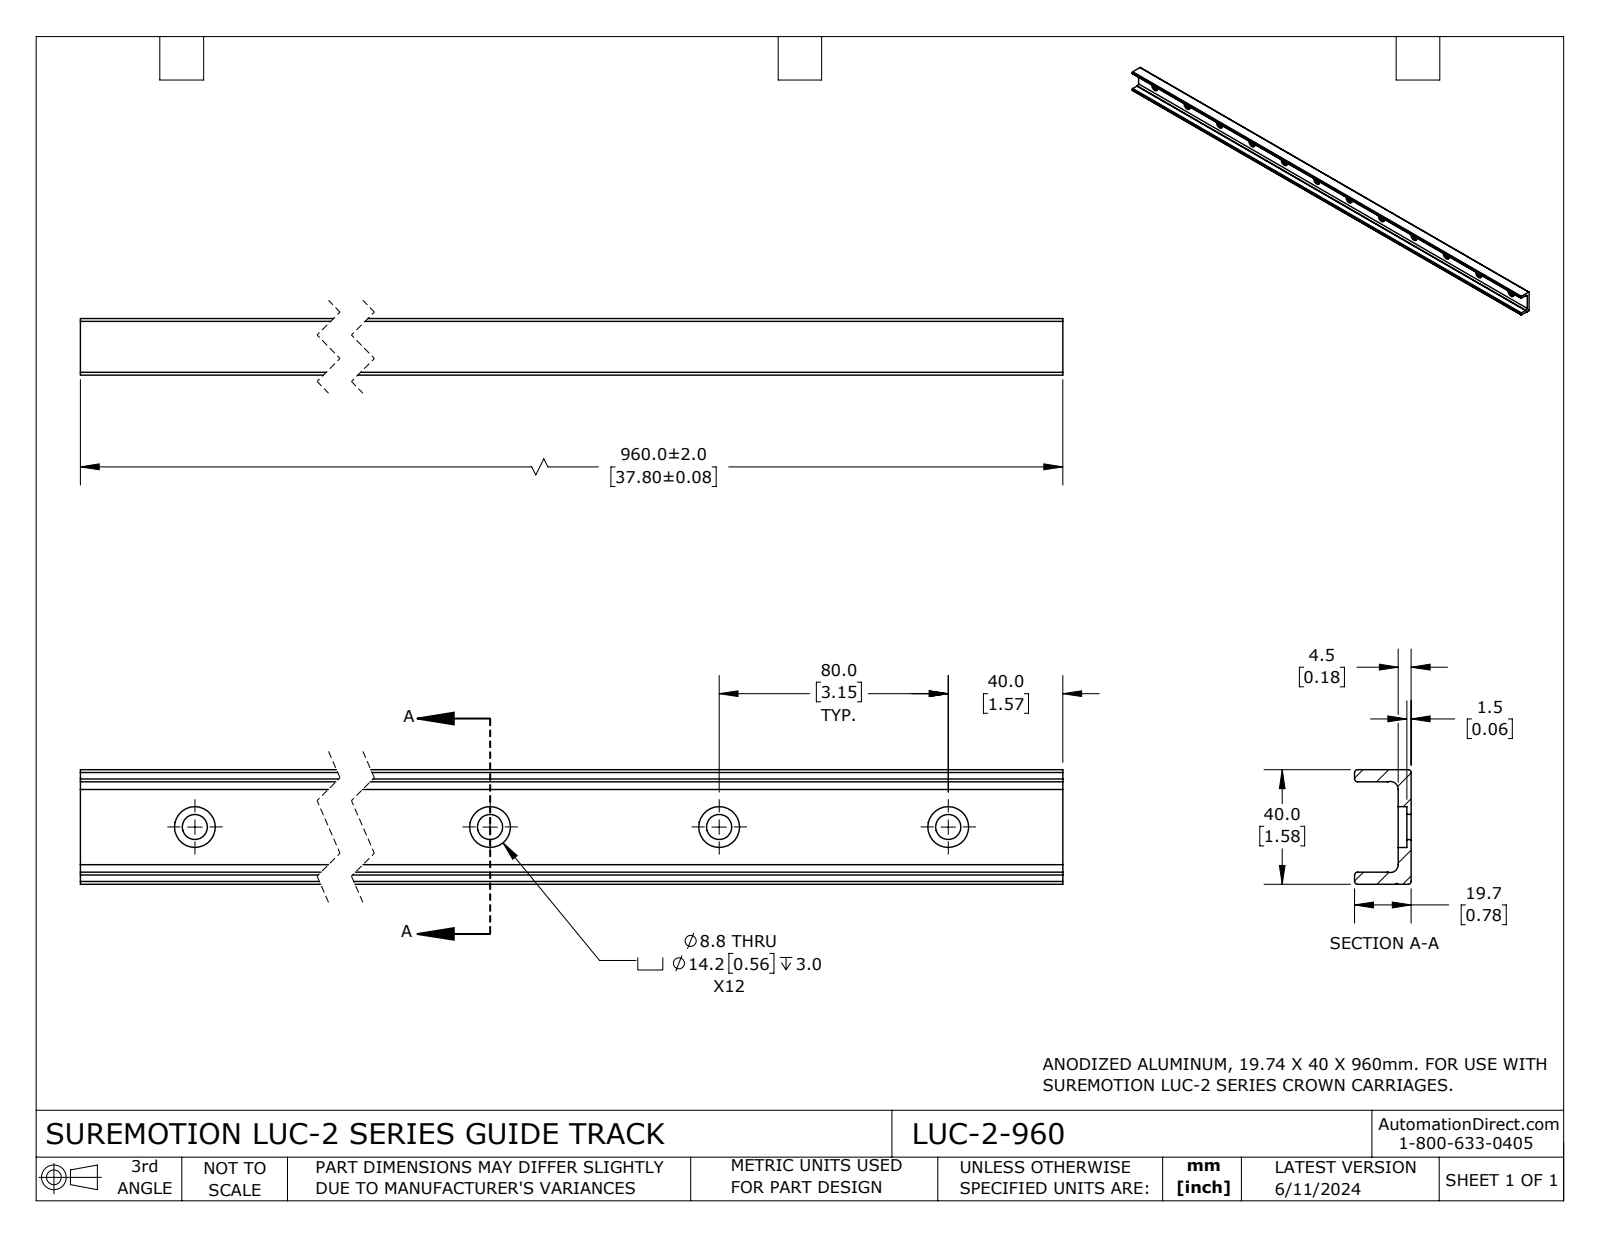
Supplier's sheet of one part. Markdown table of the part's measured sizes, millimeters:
| quantity | value |
| --- | --- |
| part name | LUC-2-960 |
| STEP written by | SolidWorks 2023 (CONFIG_CONTROL_DESIGN) |
| units | millimeters |
| bodies | 1 solid, 82 faces (23 planar, 59 cylindrical, 0 other) |
| overall size | 960 × 40.01 × 19.74 |
| volume | 291 320 mm³ |
| surface area | 141 193 mm² |
| round holes (diameter × count) | 8.81 × 12, 14.25 × 12 |
| partial cylindrical surfaces (radius × count) | 0.99 × 8, 2.77 × 2, 0.33 × 1 |
| main face-to-face distances | 4.5, 4.26, 35.76, 40.02, 31.5, 19.74, 15.24, 1.5, 3, 18.24 |
| hole center spacings | 80, 160, 240, 320, 400, 480, 560, 640 |
